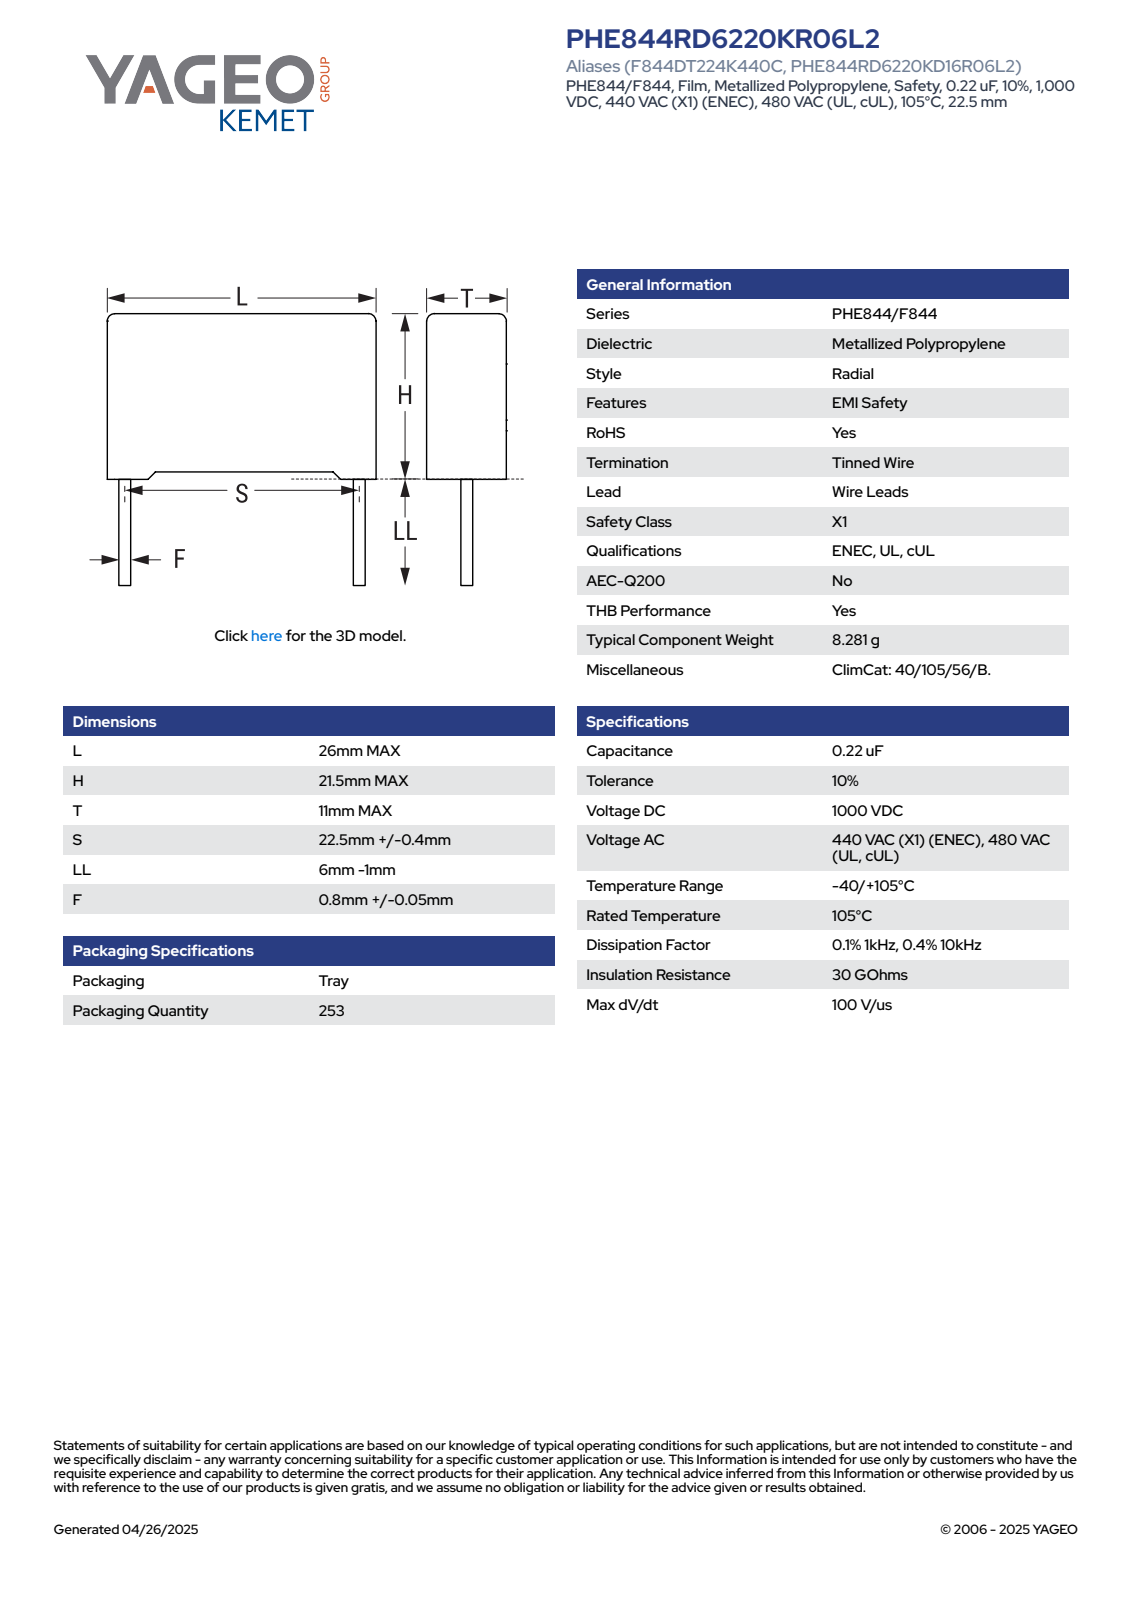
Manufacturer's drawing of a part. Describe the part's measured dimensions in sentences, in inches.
The part is named "CFR_RB2_26X21.5X11_L26H21.5T11S22.5LL5F0.85". Its 3-D file was written by "SolidWorks 2021 (AUTOMOTIVE_DESIGN)". It is 4 solids with 85 faces: 77 planar, 8 cylindrical and 0 other. Overall it measures 1.043 by 1.024 by 0.433 inches. Its volume is 0.364 cubic inches and its surface area 3.447 square inches. Round bosses or shafts: 2 of diameter 0.033. Partial cylindrical surfaces (rounded edges, fillets, slot ends): 4 of radius 0.02. The main face-to-face distances are 0.433, 1.024, 0.817, 0.817, 0.029, 0.03, 0.846, 0.034, 0.989, 0.399.
